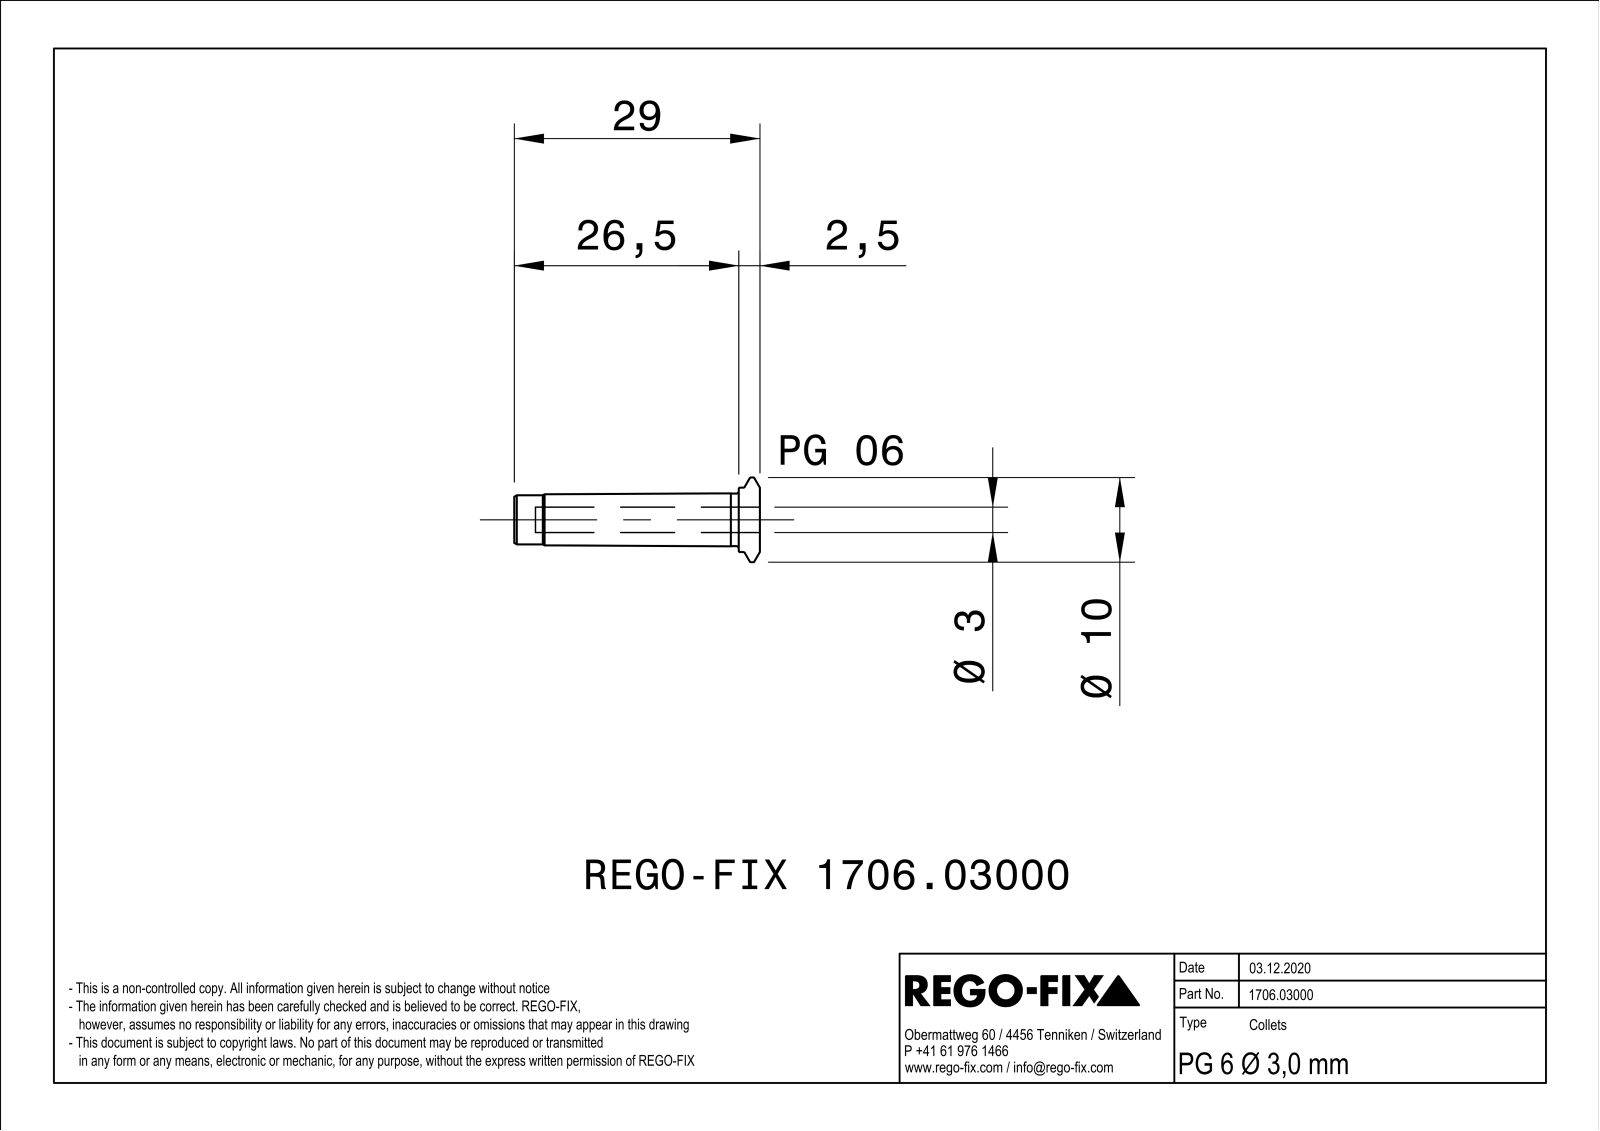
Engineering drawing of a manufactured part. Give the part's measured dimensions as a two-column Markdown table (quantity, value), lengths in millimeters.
| quantity | value |
| --- | --- |
| part name | NOCUT |
| STEP written by | SIEMENS PLM Software Solid Edge ST10 (AUTOMOTIVE_DESIGN) |
| units | millimeters |
| bodies | 1 solid, 62 faces (16 planar, 12 cylindrical, 34 other) |
| overall size | 29 × 10 × 9.99 |
| volume | 667 mm³ |
| surface area | 1 095 mm² |
| round holes (diameter × count) | 3 × 1, 3.46 × 1 |
| round bosses / shafts (diameter × count) | 10 × 1, 7.6 × 1, 6.2 × 1, 5.8 × 1 |
| main face-to-face distances | 0.45, 0.46, 29, 2.5, 26.5 |
